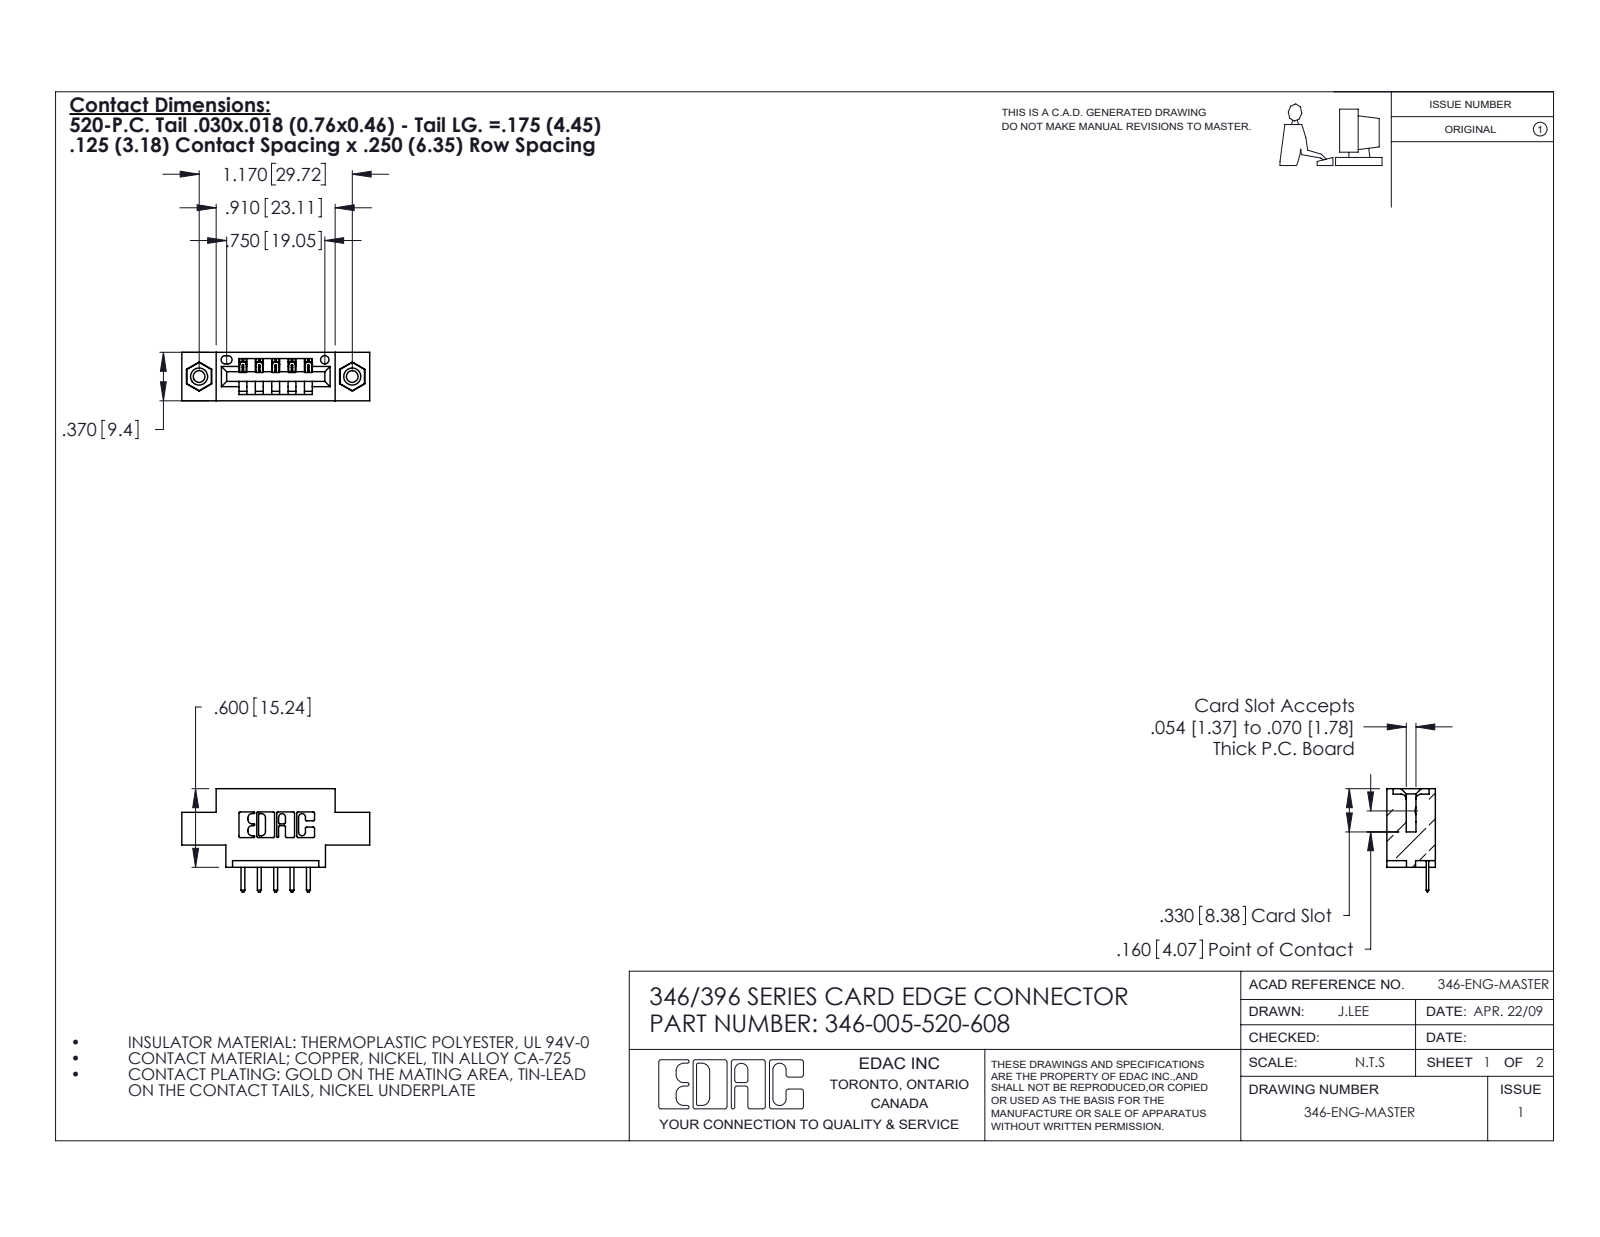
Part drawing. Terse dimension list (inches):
name: 346-005-520-608; 345-250-001_345-250-003-102; 346 Part_0.170 Offset - 0.156 Dia-TI; 345-292-001_345-293-120
written by: SolidWorks 2020 (CONFIG_CONTROL_DESIGN)
unit: in
bodies: 8 solids, 496 faces (322 planar, 158 cylindrical, 16 other)
size: 1.435 × 0.788 × 0.37
volume: 0.187 in³; area: 5.514 in²
holes: 2× ⌀0.089, 2× ⌀0.125, 2× ⌀0.156, 1× ⌀0.064
bosses: 2× ⌀0.155
rounds: 22× R0.01, 12× R0.01, 10× R0.006, 6× R0.007, 6× R0.031, 3× R0.026, 2× R0.031, 2× R0.04
face distances: 0.37, 0.25, 0.048, 0.322, 0.222, 0.148, 0.1, 0.174, 0.55, 0.125
hole spacings: 0.246, 0.969, 1.17
